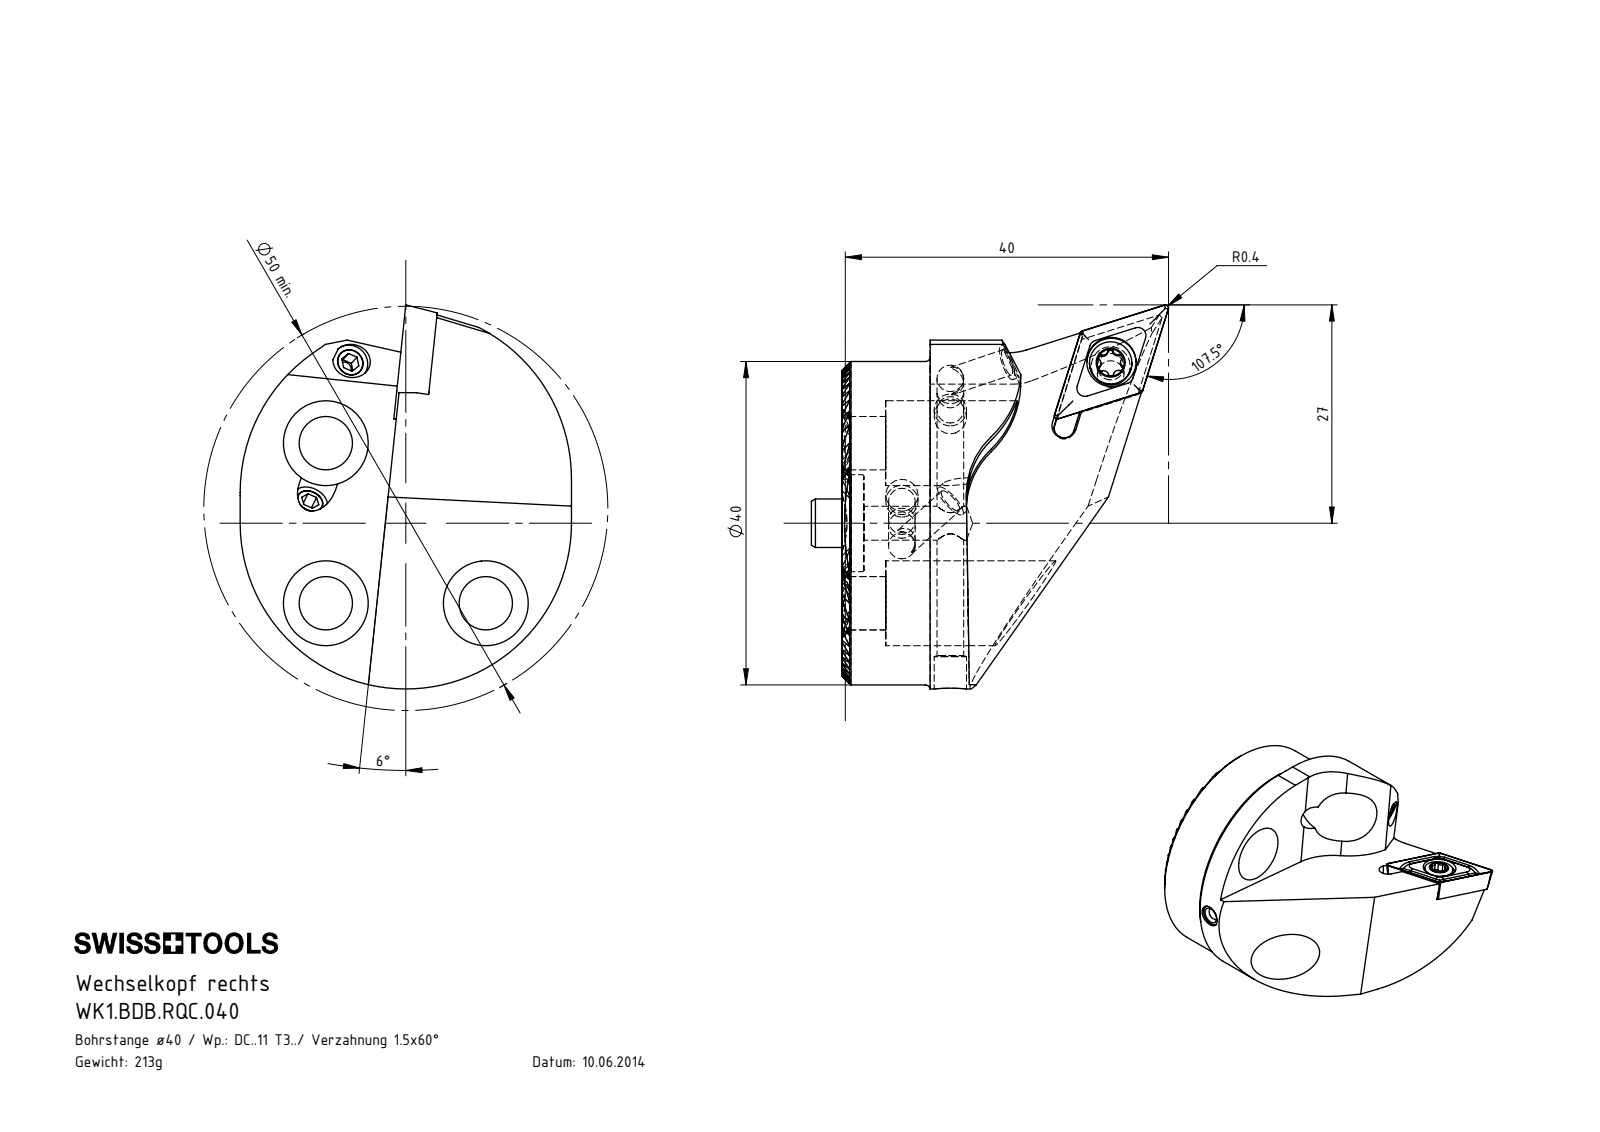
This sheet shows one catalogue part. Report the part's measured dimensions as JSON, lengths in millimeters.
{"part_name": "KVT_MB_600_040; WK1-BDB.RQC.040_A; DCMT11T304; WK1.BDB.RQC.040 (+3 more)", "step_written_by": "SolidWorks 2017 (AUTOMOTIVE_DESIGN)", "units": "millimeters", "bodies": {"solids": 12, "faces": 599, "planar": 222, "cylindrical": 206, "other": 171}, "overall_size": [47.51, 44.2, 41], "volume_mm3": 26871, "surface_area_mm2": 11553, "round_holes": [[3.3, 6], [3, 3], [6.6, 3], [10.5, 3], [1.7, 2], [4, 2], [4.5, 2], [4.2, 1], [4.4, 1], [6.1, 1], [12, 1]], "round_bosses_or_shafts": [[4, 6], [40, 1], [6, 1], [5.25, 1]], "partial_cylinders_radius": [[0.12, 26], [0.34, 6], [0.59, 6], [21, 2], [1.25, 1], [7, 1], [10, 1], [12, 1]], "face_to_face_distances": [1.3, 2.6, 3.9, 12.99, 5.2, 11.69, 9.09, 10.39, 7.79, 6.5], "hole_center_spacings": [14, 19.8, 28]}
